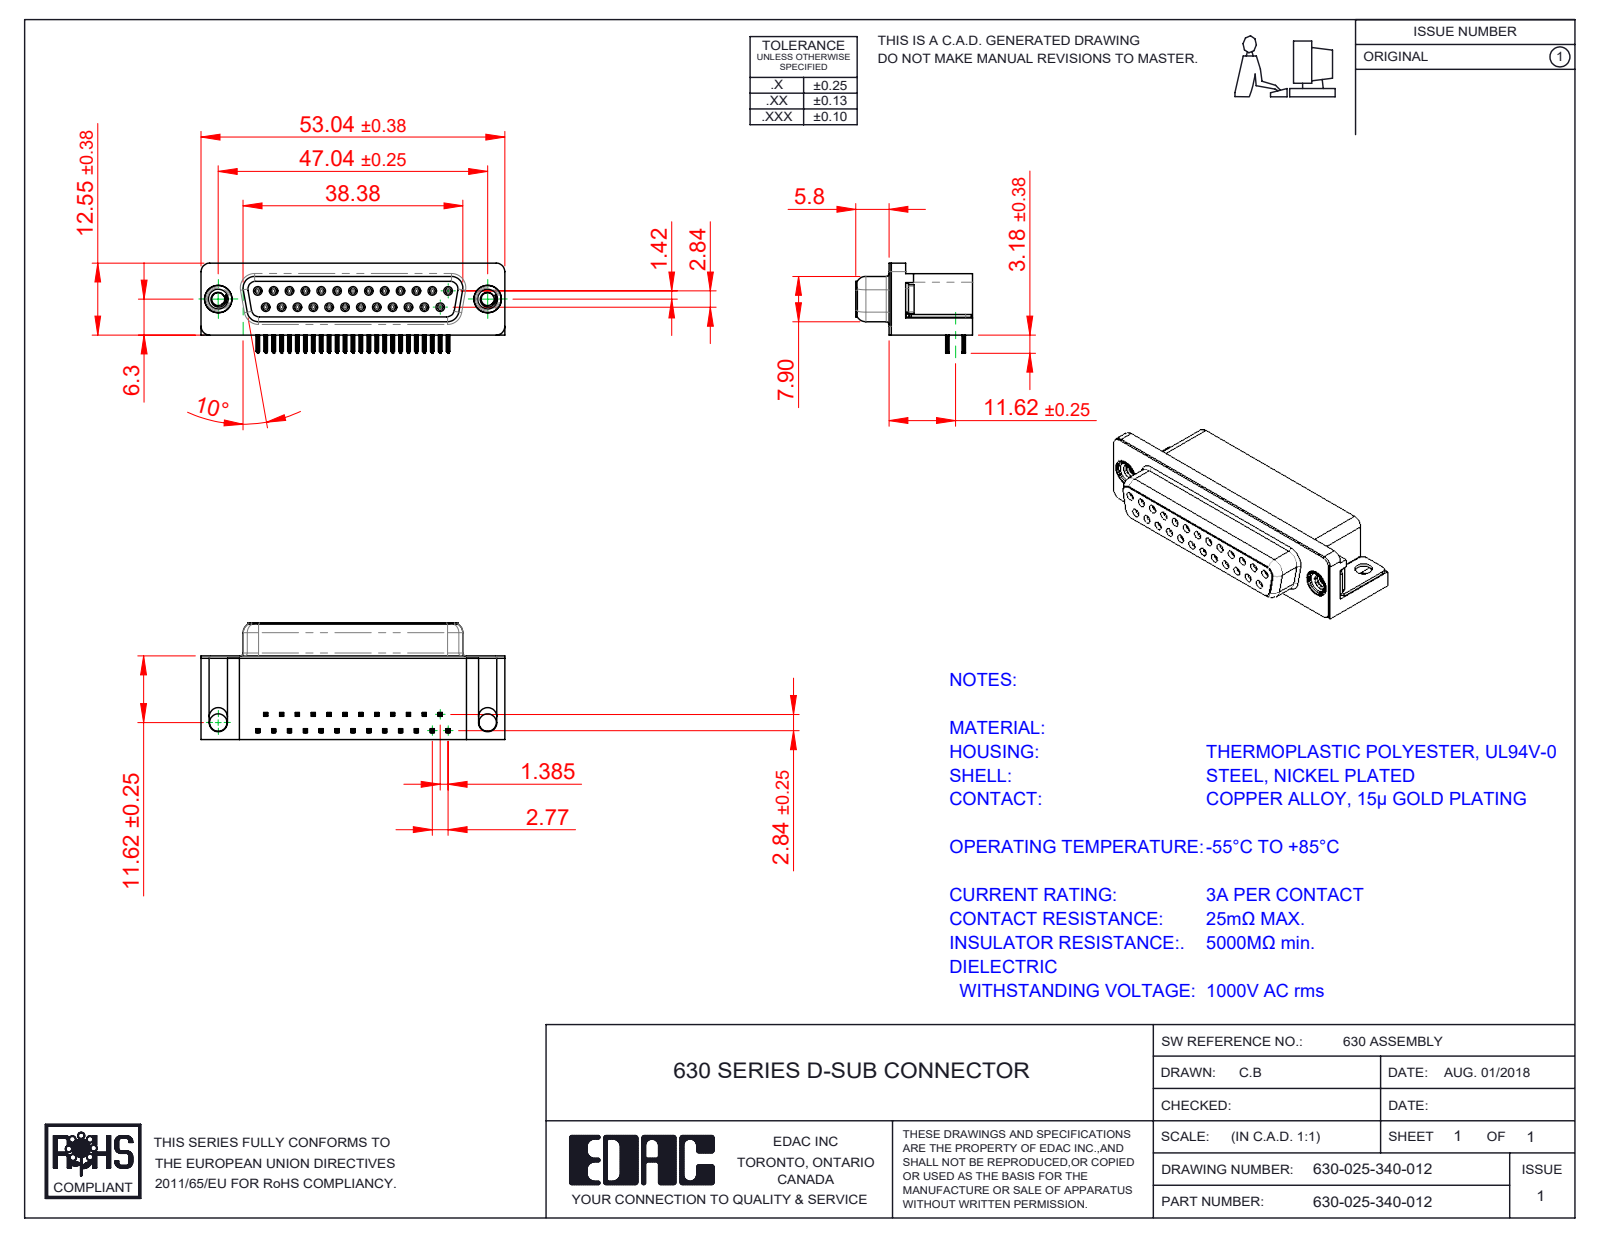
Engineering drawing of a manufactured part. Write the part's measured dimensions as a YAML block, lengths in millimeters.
part_name: "630 Contact Top; 630 Contact Bottom; 630-025-340-012; 630 4-40 Threaded Rivet (+3 more)"
step_written_by: "SolidWorks 2020 (CONFIG_CONTROL_DESIGN)"
units: millimeters
bodies: {solids: 31, faces: 3850, planar: 1722, cylindrical: 920, other: 1208}
overall_size: [53.04, 20.4, 15.73]
volume: 8589
surface_area: 10074
round_holes:
  - {diameter: 0.8, count: 25}
  - {diameter: 0.9, count: 25}
  - {diameter: 2.26, count: 2}
  - {diameter: 3.05, count: 2}
  - {diameter: 4, count: 2}
  - {diameter: 4.8, count: 2}
  - {diameter: 5, count: 2}
round_bosses_or_shafts:
  - {diameter: 1.2, count: 25}
  - {diameter: 4.9, count: 2}
  - {diameter: 4.75, count: 2}
  - {diameter: 3.9, count: 2}
partial_cylinders:
  - {radius: 0.1, count: 200}
  - {radius: 0.15, count: 100}
  - {radius: 0.35, count: 50}
  - {radius: 0.34, count: 25}
  - {radius: 1, count: 18}
  - {radius: 0.28, count: 12}
  - {radius: 0.25, count: 8}
  - {radius: 1.35, count: 8}
face_to_face_distances: [0.4, 6.2, 10.35, 14.2, 2.73, 6.65, 0.85, 14.6, 2.84, 5.8]
hole_center_spacings: [3.16, 2.77, 5.54, 8.31, 11.08, 5.03, 5.04, 7.48]
